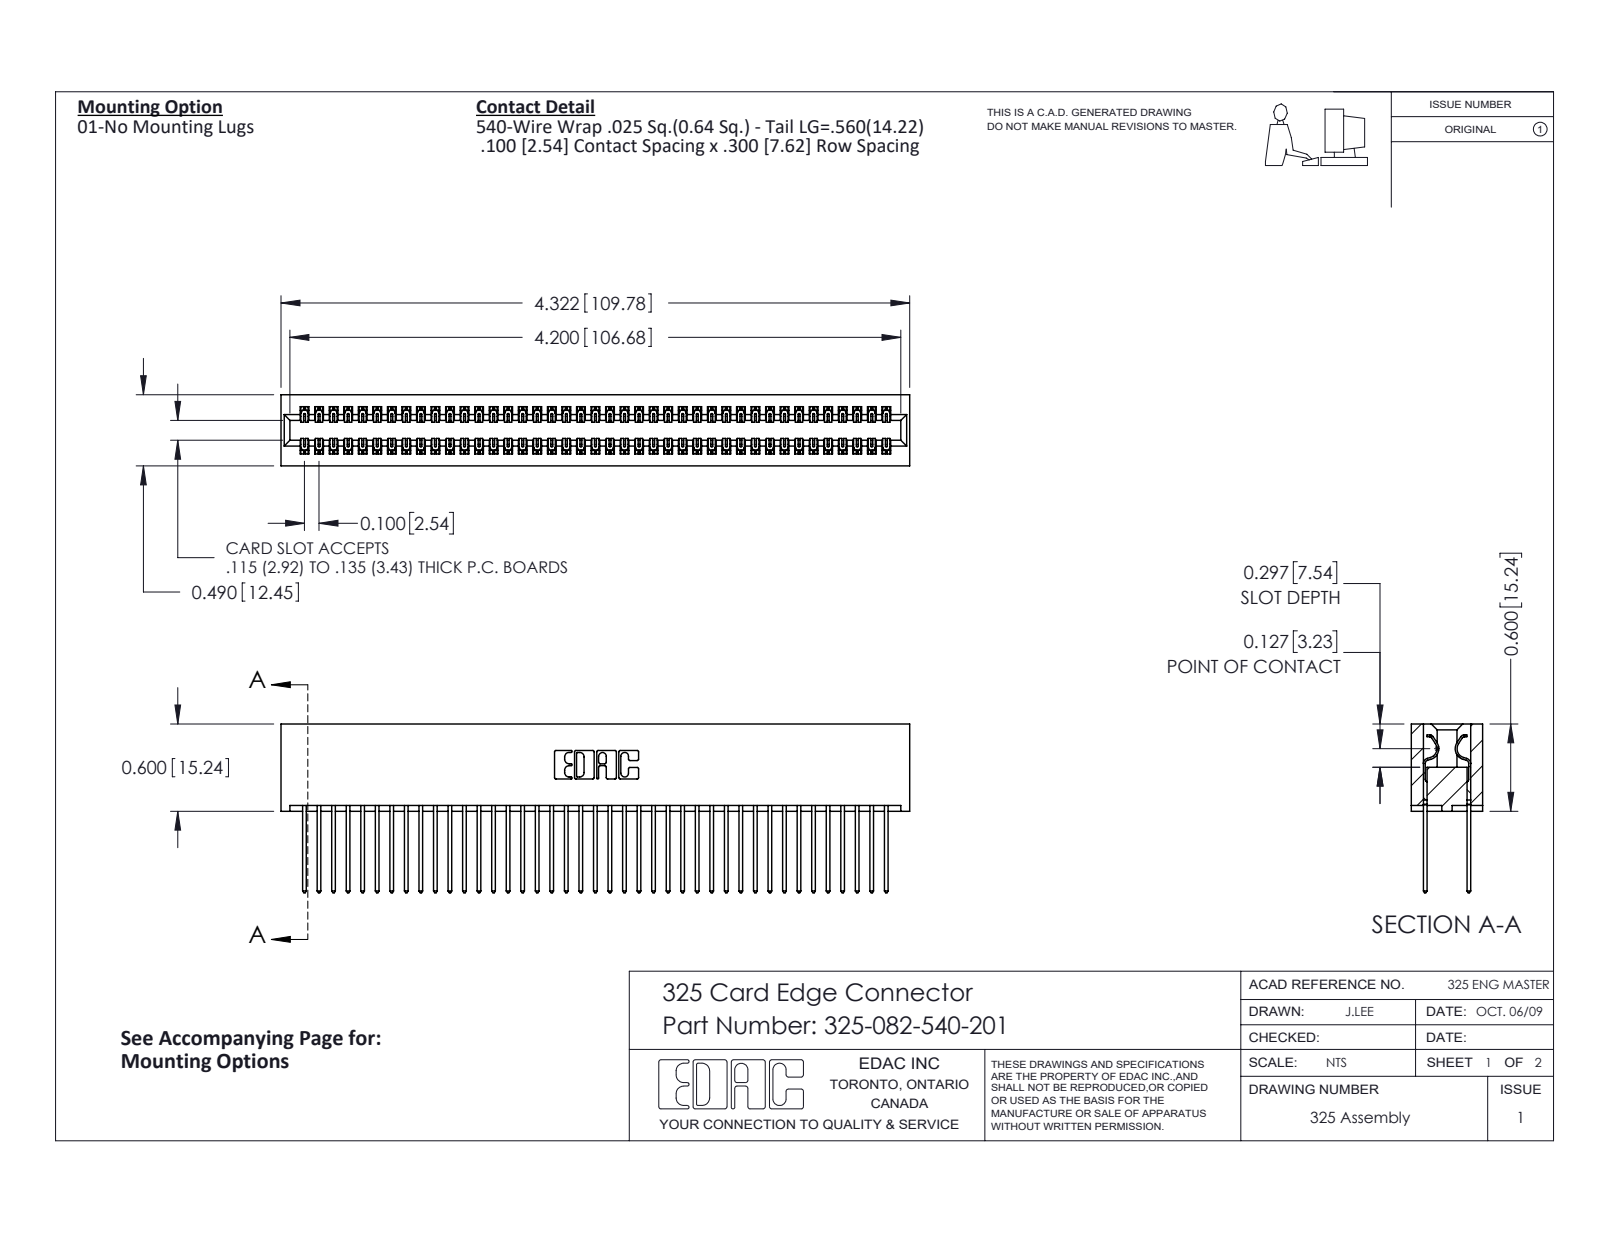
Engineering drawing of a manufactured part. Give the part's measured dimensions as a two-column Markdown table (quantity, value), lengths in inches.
| quantity | value |
| --- | --- |
| part name | 325 Part_Lugless; 325-082-540-201; 325-292-001_325-293-140 |
| STEP written by | SolidWorks 2016 (CONFIG_CONTROL_DESIGN) |
| units | inches |
| bodies | 83 solids, 4370 faces (3018 planar, 1352 cylindrical, 0 other) |
| overall size | 4.322 × 1.16 × 0.49 |
| volume | 0.92 in³ |
| surface area | 31.57 in² |
| partial cylindrical surfaces (radius × count) | 0.006 × 123, 0.01 × 82, 0.01 × 22, 0.007 × 6, 0.031 × 6, 0.026 × 3, 0.014 × 2, 0.022 × 2 |
| main face-to-face distances | 0.083, 0.407, 0.3, 0.107, 0.383, 0.025, 0.325, 0.49, 0.275, 0.56 |
